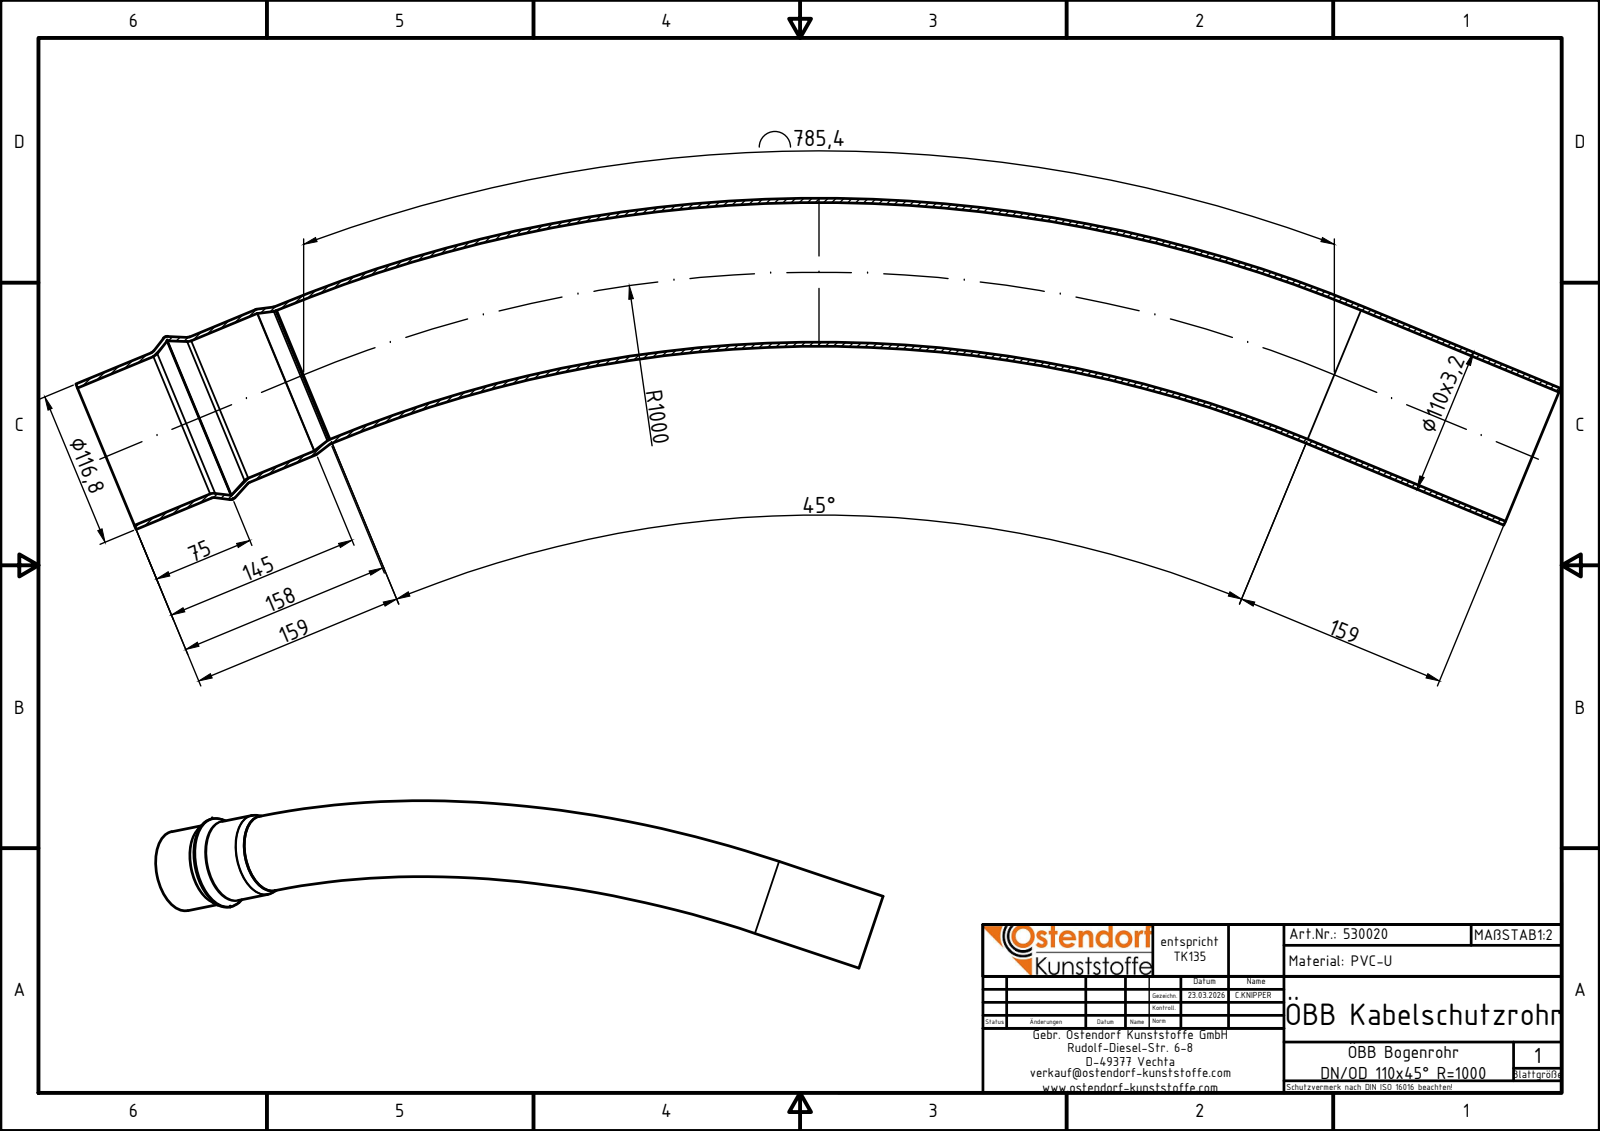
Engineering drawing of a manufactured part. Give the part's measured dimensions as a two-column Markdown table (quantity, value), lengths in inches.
| quantity | value |
| --- | --- |
| part name | 530020z |
| STEP written by | Autodesk Inventor 2024 (AUTOMOTIVE_DESIGN) |
| units | inches |
| bodies | 1 solid, 32 faces (2 planar, 10 cylindrical, 20 other) |
| overall size | 40.056 × 20.057 × 5.138 |
| volume | 73.35 in³ |
| surface area | 1 167 in² |
| round holes (diameter × count) | 4.078 × 2, 4.346 × 1, 4.886 × 1 |
| round bosses / shafts (diameter × count) | 4.331 × 2, 5.138 × 1, 4.598 × 1 |
